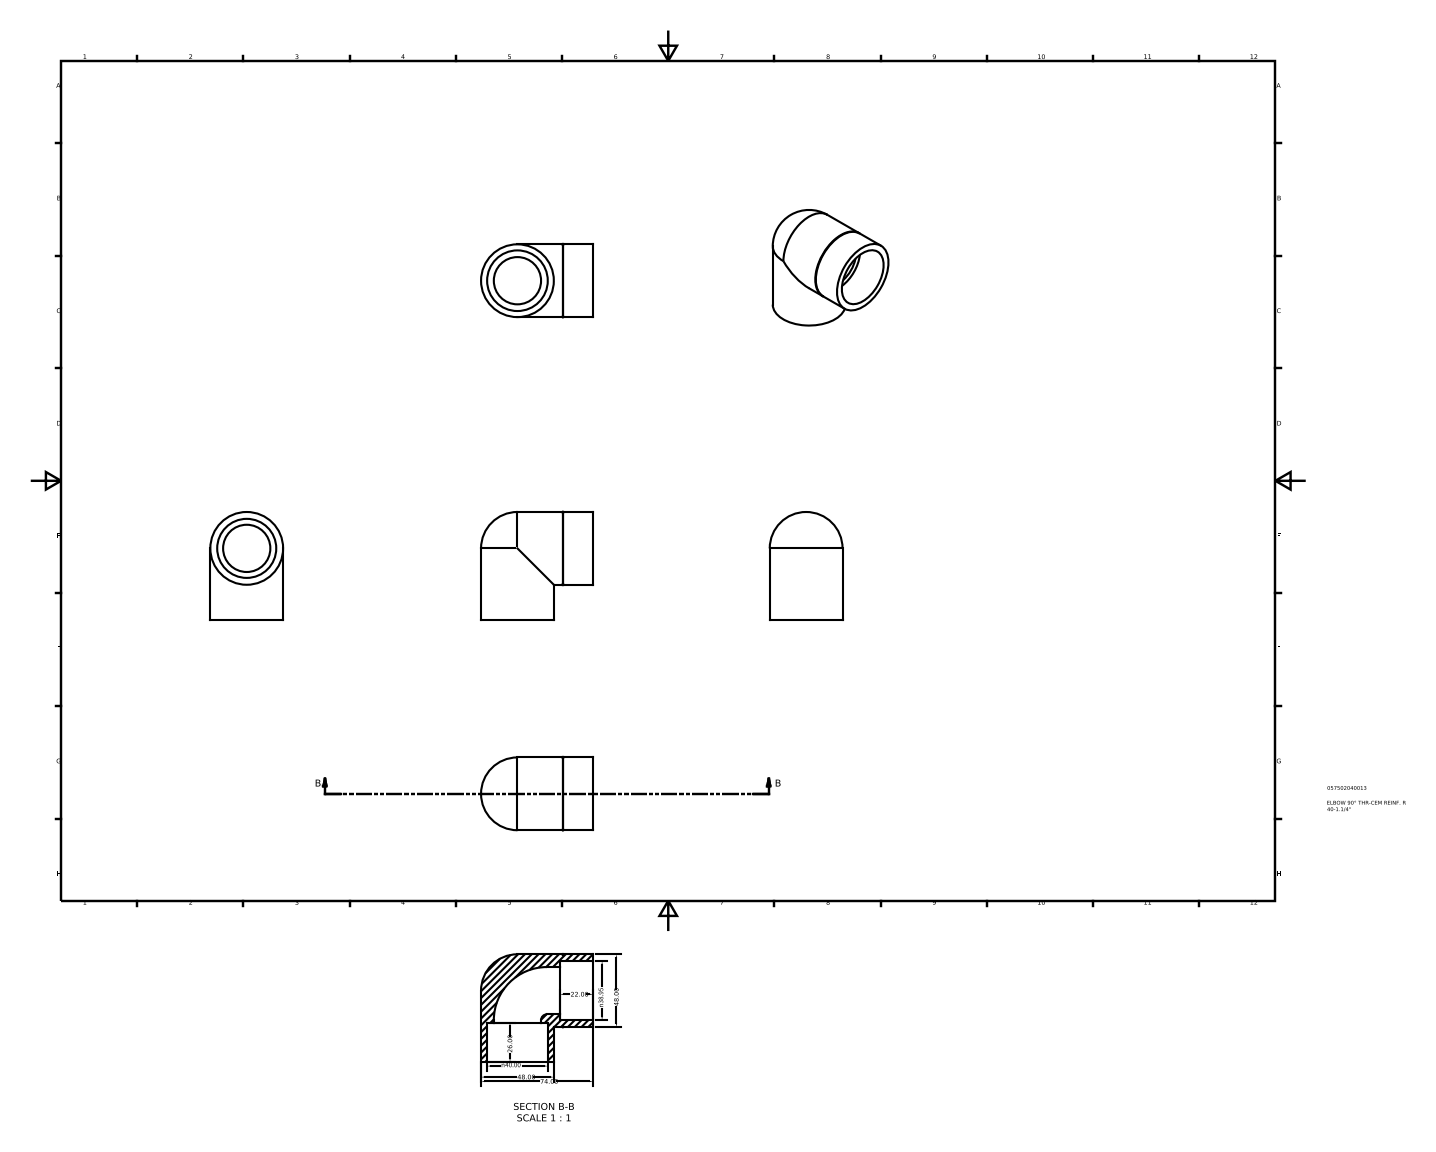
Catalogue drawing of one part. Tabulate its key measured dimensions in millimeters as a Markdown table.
| quantity | value |
| --- | --- |
| part name | 057502040013 |
| STEP written by | Autodesk Inventor 2015 (AUTOMOTIVE_DESIGN) |
| units | millimeters |
| bodies | 1 solid, 15 faces (4 planar, 7 cylindrical, 4 other) |
| overall size | 74 × 71 × 48 |
| volume | 81 669 mm³ |
| surface area | 26 256 mm² |
| round holes (diameter × count) | 31.16 × 2, 38.95 × 1, 40 × 1 |
| round bosses / shafts (diameter × count) | 48 × 2 |
| main face-to-face distances | 26, 22 |
